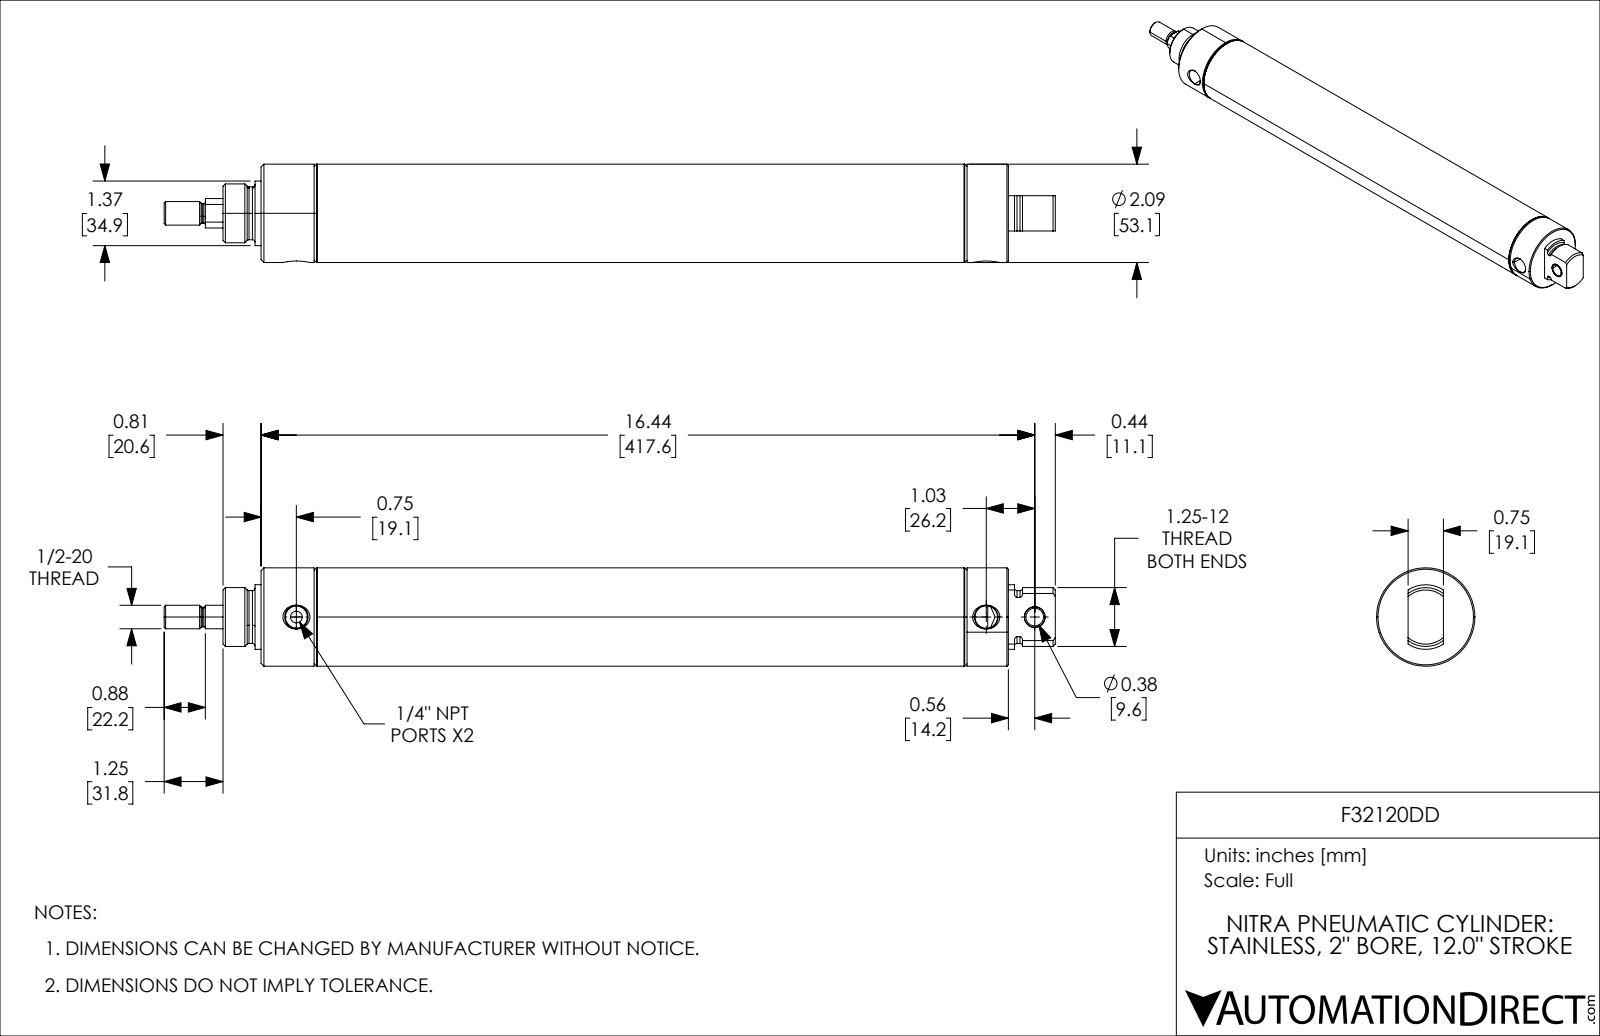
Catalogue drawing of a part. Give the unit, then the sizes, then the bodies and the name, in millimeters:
Units: millimetres
Overall size (bounding box): 481.02 × 53.09 × 53.09
Round holes (diameter × count): ⌀6.35 ×1, ⌀9.55 ×1, ⌀11.15 ×1, ⌀12.18 ×1, ⌀16.52 ×1, ⌀19.05 ×1, ⌀49.05 ×1
Round bosses / shafts (diameter × count): ⌀53.09 ×1, ⌀51.16 ×1, ⌀34.87 ×1, ⌀31.75 ×1, ⌀28.51 ×1, ⌀15.88 ×1, ⌀12.7 ×1, ⌀11.15 ×1
Partial cylindrical surfaces — rounded edges, fillets, slot ends (radius × count): R14.25 ×1
Main face-to-face distances: 30.17, 304.8, 334.97, 365.2, 60.4, 30.23, 334.98, 30.18, 30.22, 38.15
Hole centre spacings: 26.16, 26.17, 372.36, 398.52, 398.53
Volume: 344 263 mm³ · Surface area: 177 071 mm²
Bodies: 5 solids, 160 faces (31 planar, 60 cylindrical, 69 other)
Part name (STEP PRODUCT): F32120DD_11; F32120DD_5; F32120DD_7; F32120DD_3 (+2 more)
STEP written by: SolidWorks 2021 (CONFIG_CONTROL_DESIGN)
